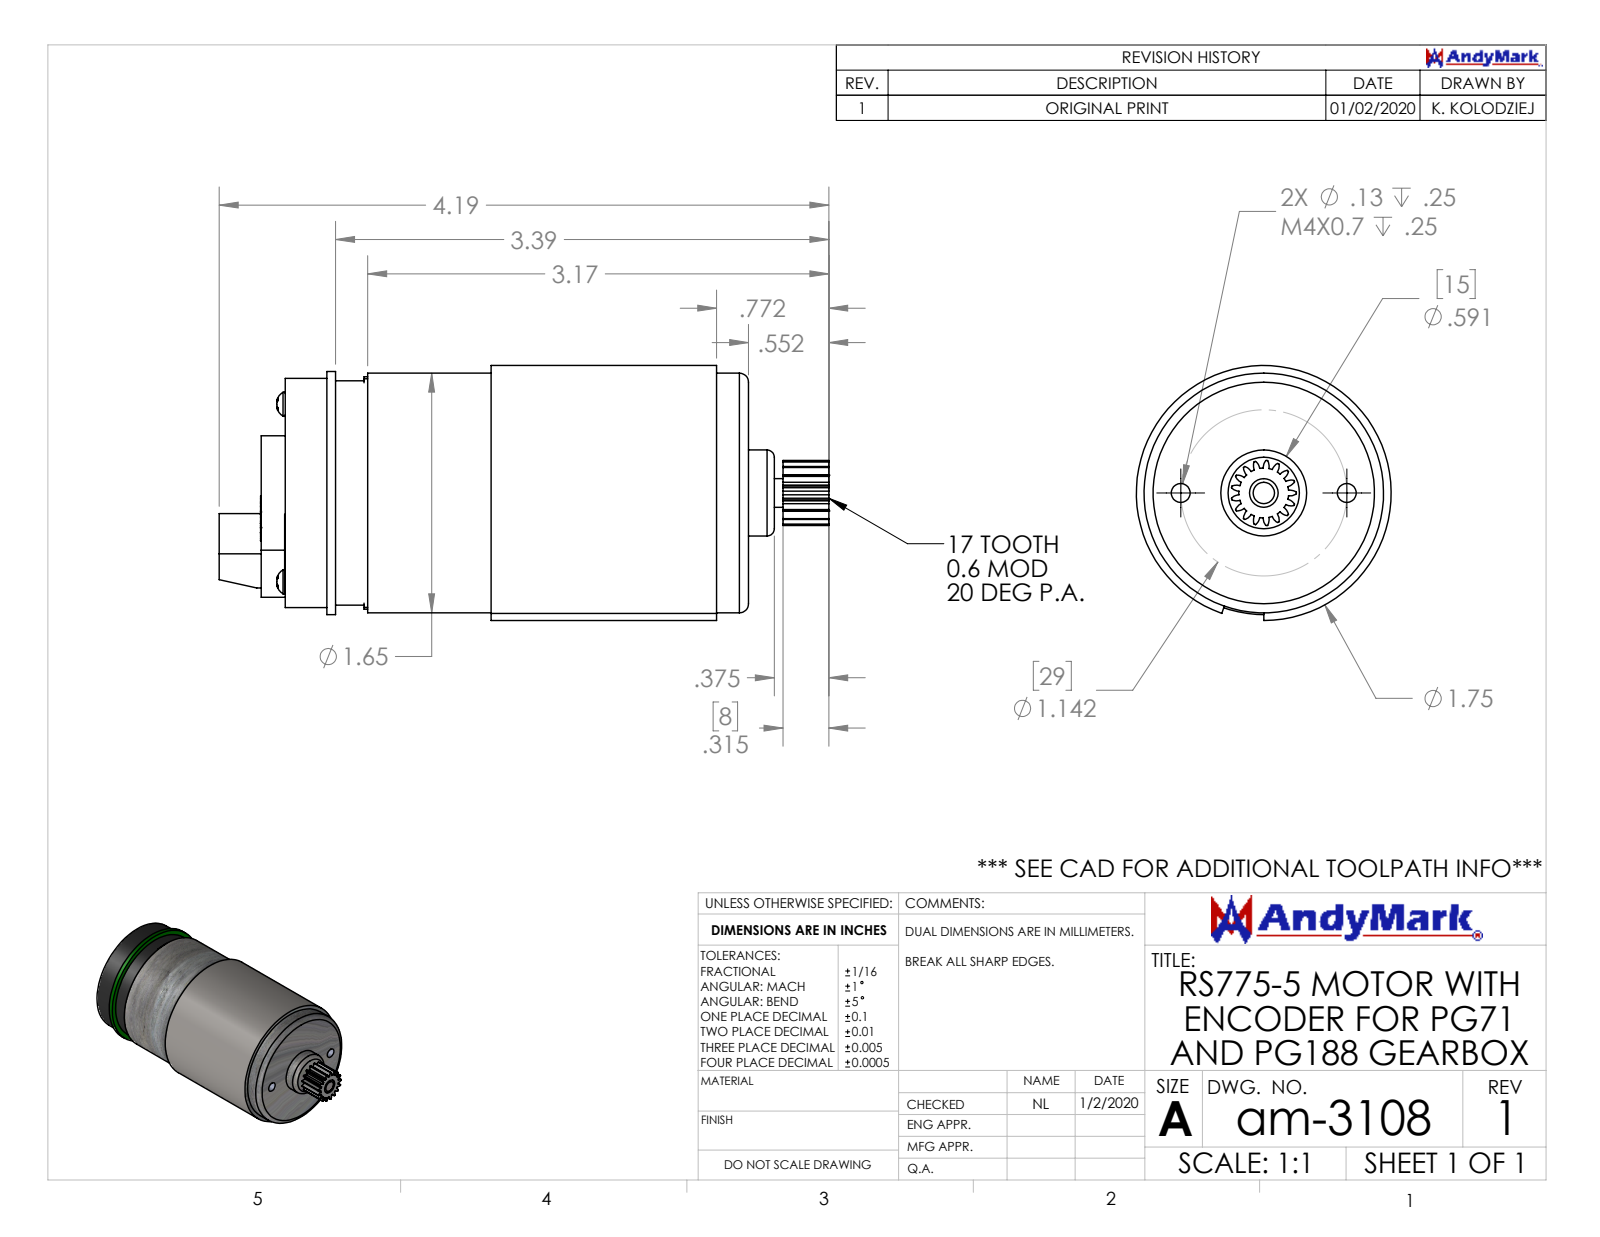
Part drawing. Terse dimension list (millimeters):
name: 17T 0.6MOD 5mm; RS775-5 with Encoder; am-3108 RS775-5 Motor with Encoder for PG71 and PG188 Gearbox
written by: SolidWorks 2024 (CONFIG_CONTROL_DESIGN)
unit: mm
bodies: 5 solids, 690 faces (317 planar, 194 cylindrical, 179 other)
size: 106.44 × 44.5 × 44.5
volume: 42 680 mm³; area: 32 152 mm²
holes: 2× ⌀3.18, 2× ⌀3.3, 1× ⌀5.44, 1× ⌀6.35, 1× ⌀40.56
bosses: 2× ⌀2.18, 2× ⌀1.33, 1× ⌀44.5, 1× ⌀42.44, 1× ⌀41.83, 1× ⌀40.01, 1× ⌀39.17, 1× ⌀38.66
rounds: 34× R2.04, 16× R1.4, 1× R4.35, 1× R5.7, 1× R9.27, 1× R9.97, 1× R12.1
face distances: 1.02, 61.42, 60.4, 3.18, 64.6, 63.58, 16.29, 17.31, 77.71, 80.89
hole spacings: 13.46, 14.5, 4.98, 8.31, 13.08, 24.73, 26.71, 29
